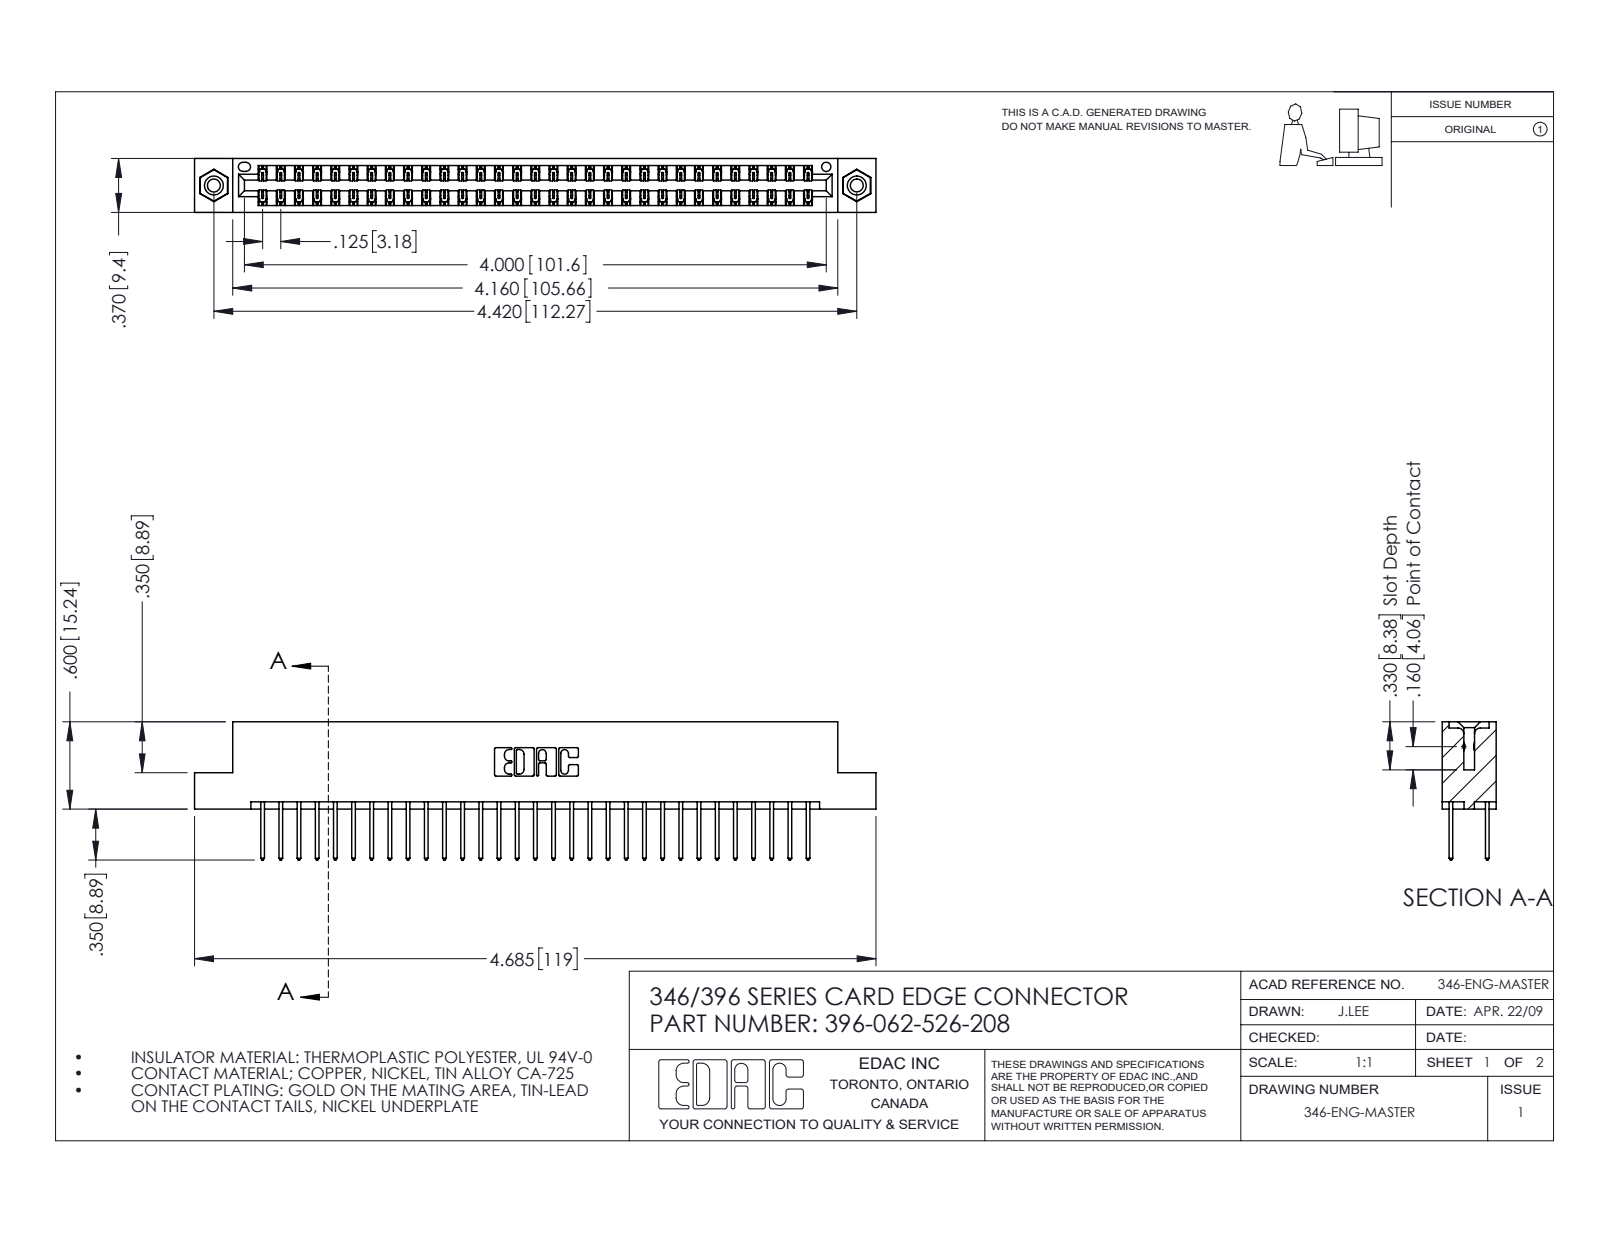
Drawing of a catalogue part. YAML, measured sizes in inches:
part_name: "345-292-001_345-293-126; 345-250-001_345-250-003-102; 396-062-526-208; 346 Part_Flush Mounting Lugs - 0.156 Dia-TI"
step_written_by: "SolidWorks 2016 (CONFIG_CONTROL_DESIGN)"
units: inches
bodies: {solids: 65, faces: 3406, planar: 2278, cylindrical: 1112, other: 16}
overall_size: [4.685, 0.95, 0.37]
volume: 0.709
surface_area: 25.21
round_holes:
  - {diameter: 0.089, count: 2}
  - {diameter: 0.125, count: 2}
  - {diameter: 0.156, count: 2}
  - {diameter: 0.064, count: 1}
round_bosses_or_shafts:
  - {diameter: 0.155, count: 2}
partial_cylinders:
  - {radius: 0.006, count: 93}
  - {radius: 0.01, count: 62}
  - {radius: 0.01, count: 22}
  - {radius: 0.007, count: 6}
  - {radius: 0.031, count: 6}
  - {radius: 0.026, count: 3}
  - {radius: 0.014, count: 2}
  - {radius: 0.022, count: 2}
face_to_face_distances: [0.048, 0.322, 0.25, 0.37, 0.072, 0.298, 0.025, 0.275, 0.148, 0.222]
hole_center_spacings: [0.246, 4.212, 4.42]
